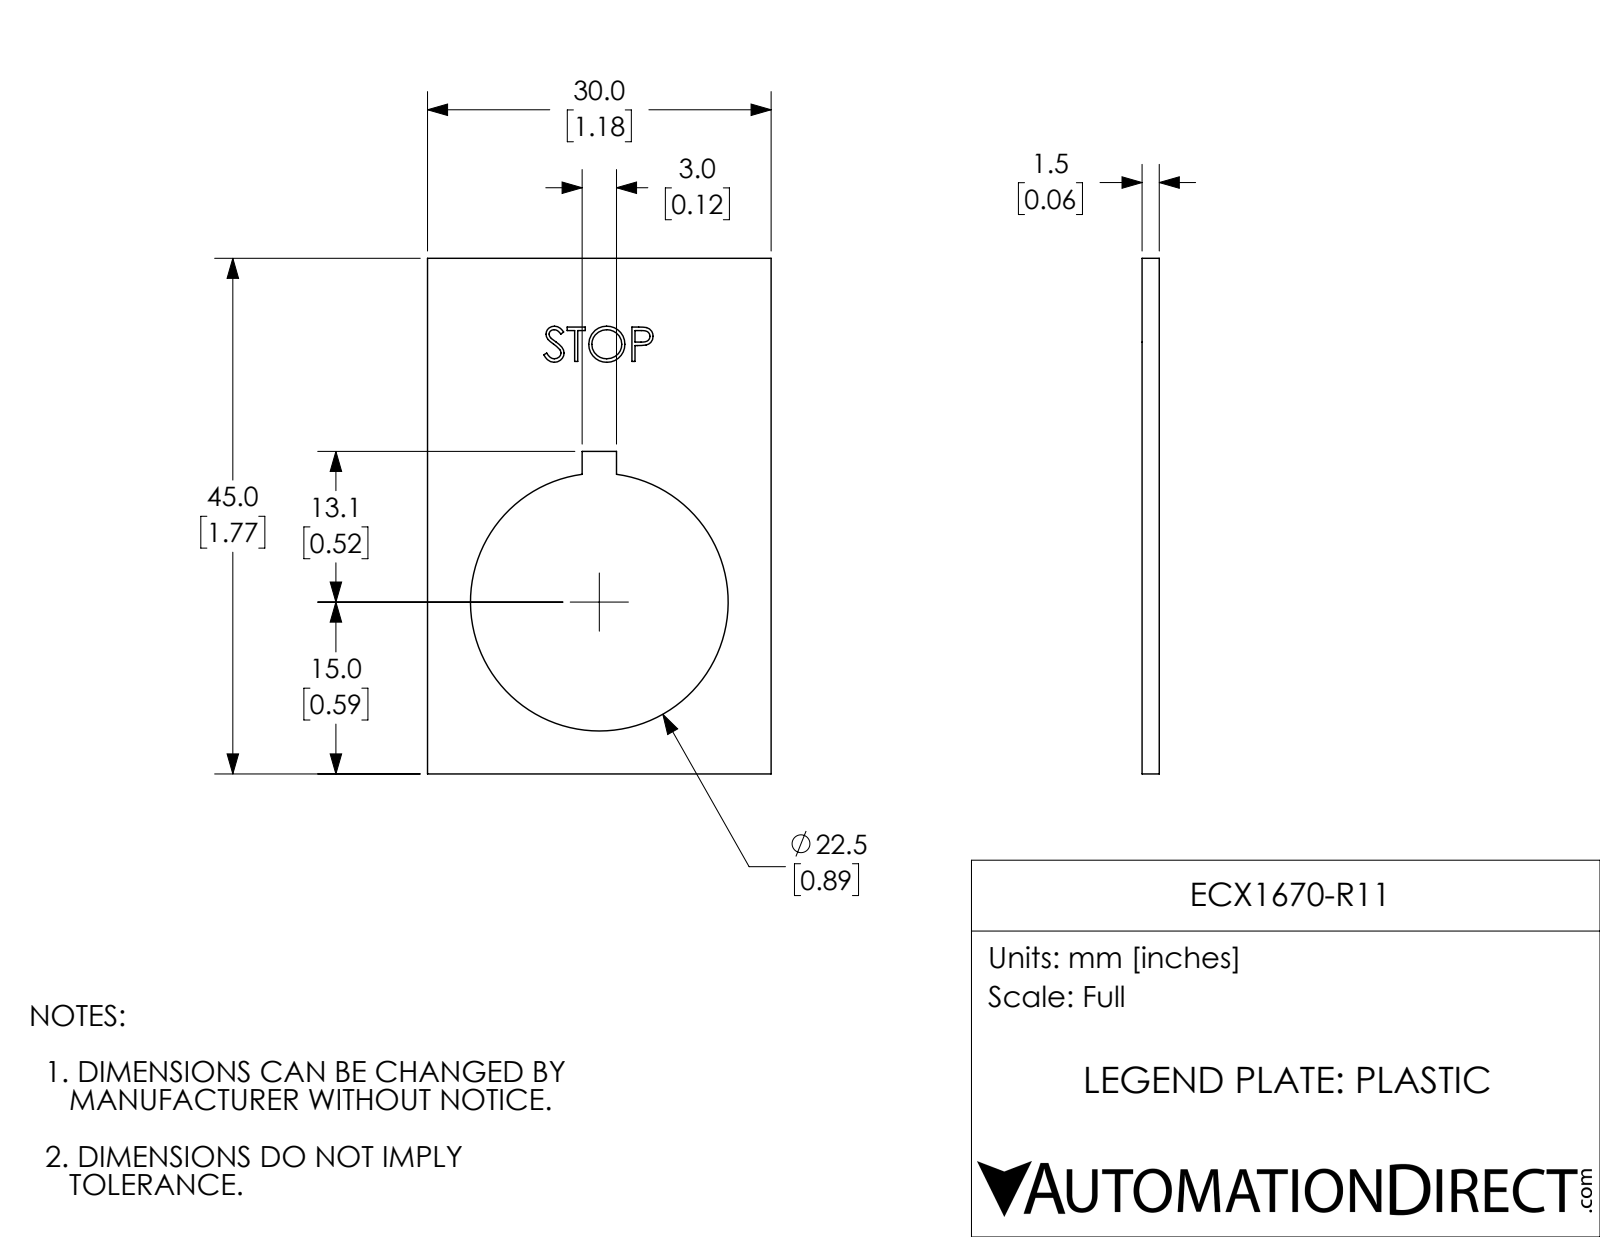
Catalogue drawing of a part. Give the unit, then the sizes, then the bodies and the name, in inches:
Units: inches
Overall size (bounding box): 1.772 × 1.181 × 0.059
Round holes (diameter × count): ⌀0.886 ×1
Main face-to-face distances: 0.059, 1.181, 1.772, 0.058, 0.531, 0.65, 1.108, 0.663, 0.118, 0.197
Volume: 0.087 in³ · Surface area: 3.459 in²
Bodies: 1 solid, 65 faces (33 planar, 3 cylindrical, 29 other)
Part name (STEP PRODUCT): ECX1670-R11
STEP written by: SolidWorks 2017 (AUTOMOTIVE_DESIGN)
